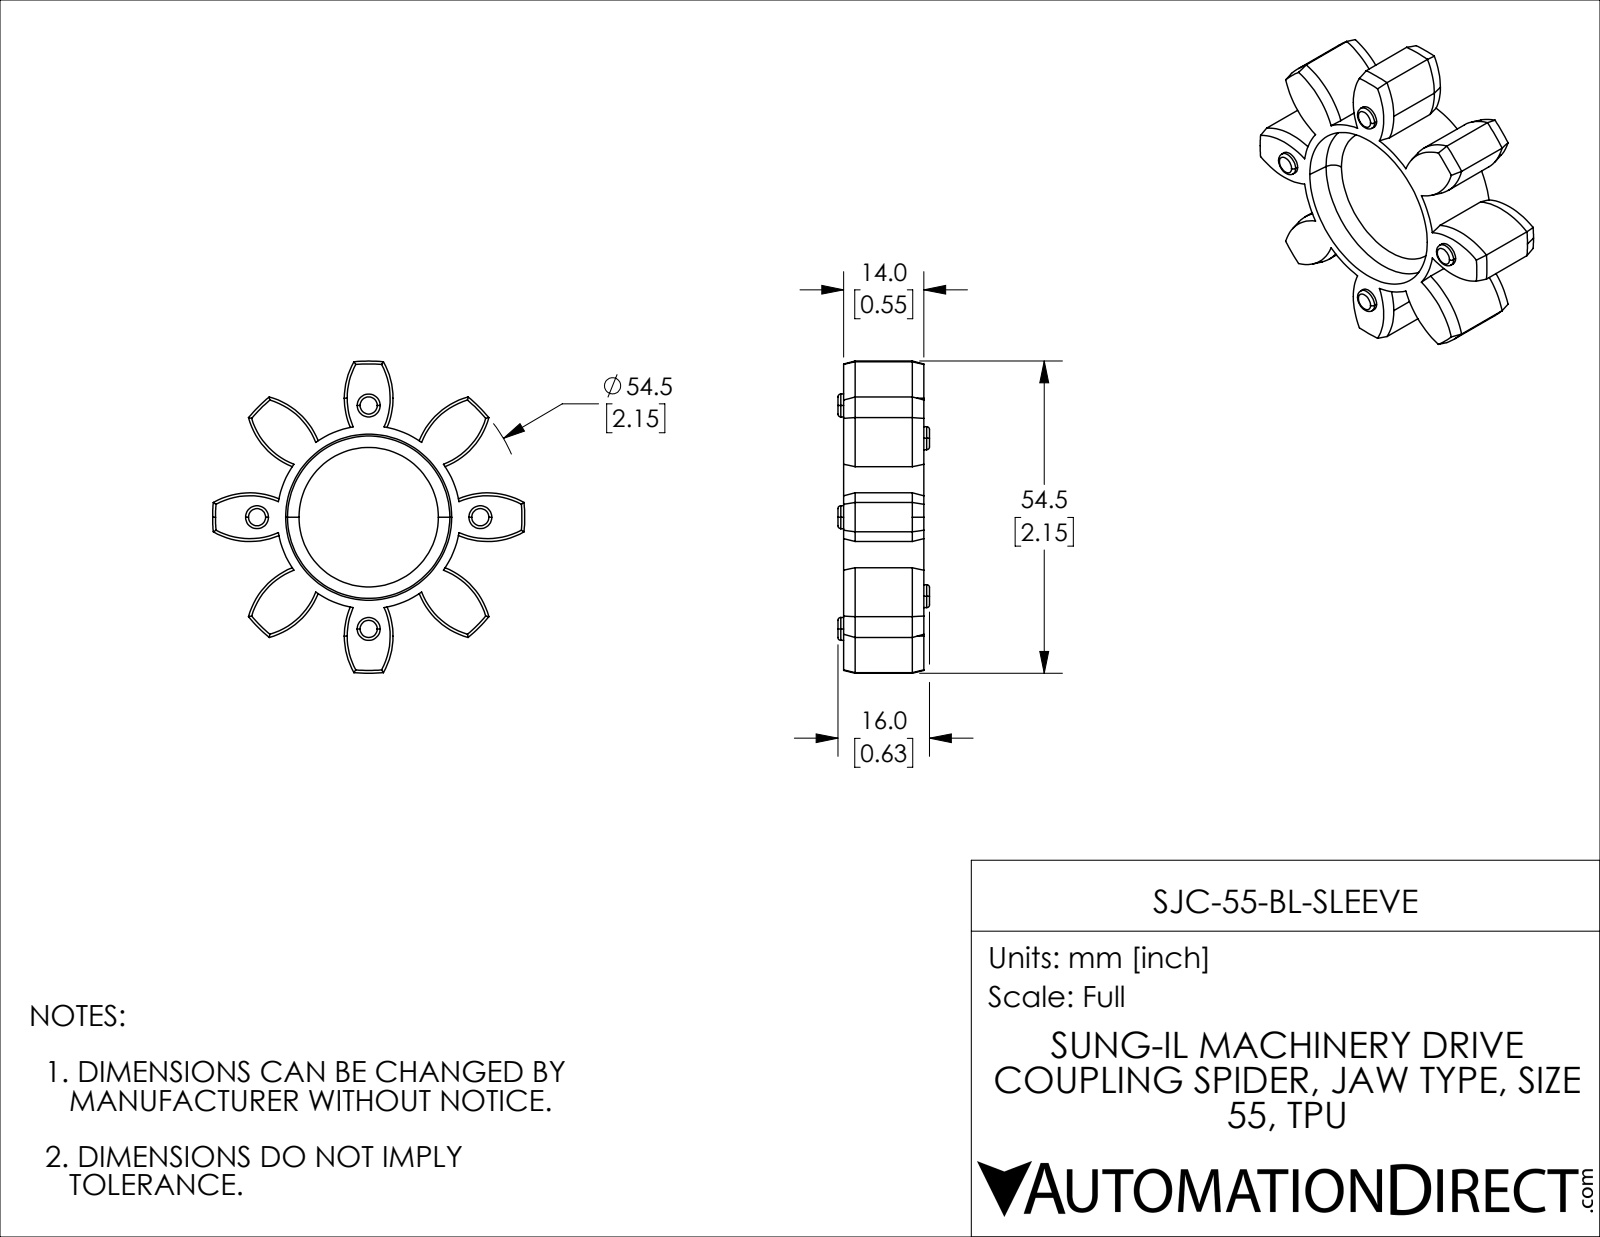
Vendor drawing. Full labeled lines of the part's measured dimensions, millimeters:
Part name (STEP PRODUCT): SJC-55-BL-SLEEVE
STEP written by: SolidWorks 2021 (CONFIG_CONTROL_DESIGN)
Units: millimetres
Bodies: 1 solid, 141 faces (12 planar, 51 cylindrical, 78 other)
Overall size (bounding box): 54.5 × 54.5 × 16
Volume: 13 854 mm³ · Surface area: 7 550 mm²
Round bosses / shafts (diameter × count): ⌀4 ×8
Partial cylindrical surfaces — rounded edges, fillets, slot ends (radius × count): R12.85 ×8, R16 ×1, R27.25 ×1
Main face-to-face distances: 5.5, 8.5, 14, 3, 1, 6.5, 9.5, 15, 16
